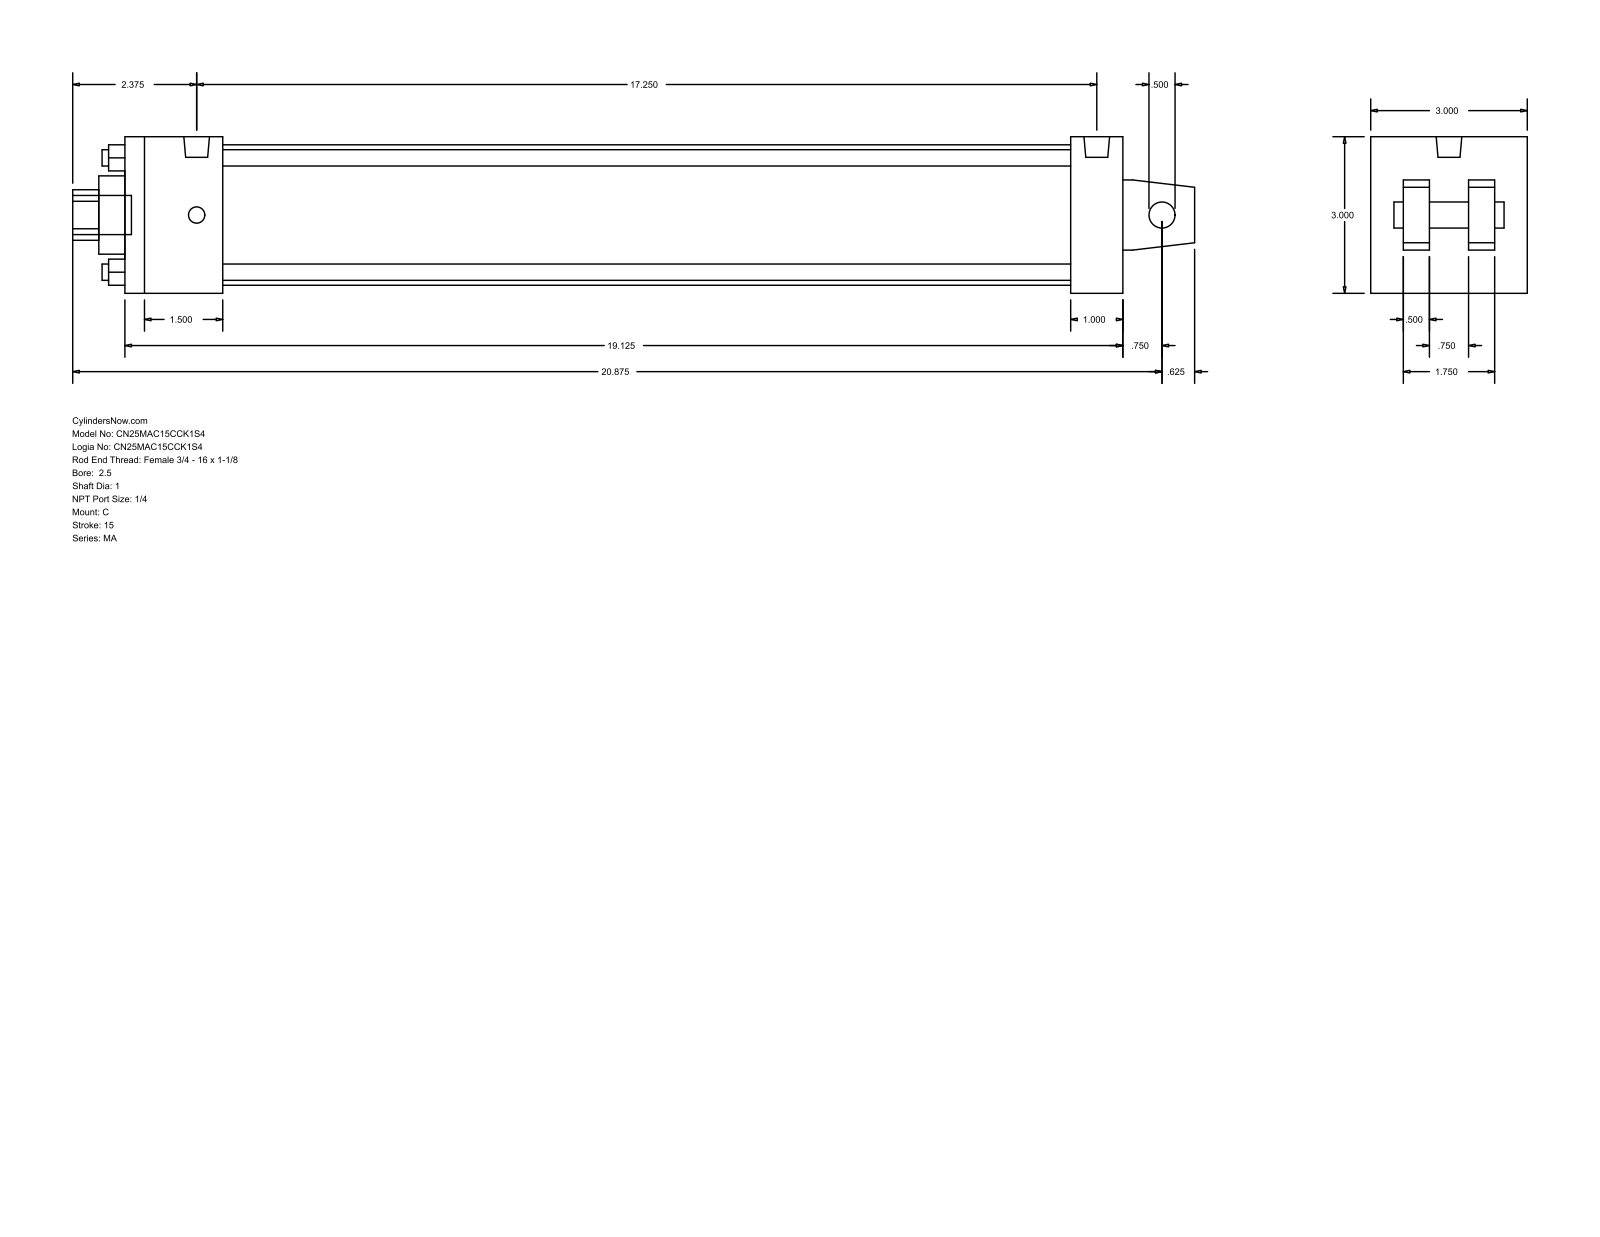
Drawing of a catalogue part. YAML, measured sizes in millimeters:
part_name: "MA_C__0250_1"
step_written_by: "GSSL Pune (CONFIG_CONTROL_DESIGN)"
units: millimeters
bodies: {solids: 0, faces: 103, planar: 76, cylindrical: 27, other: 0}
overall_size: [546.1, 76.2, 76.2]
round_holes:
  - {diameter: 7.94, count: 4}
  - {diameter: 12.7, count: 1}
  - {diameter: 25.4, count: 1}
  - {diameter: 38.1, count: 1}
  - {diameter: 68.33, count: 1}
round_bosses_or_shafts:
  - {diameter: 7.94, count: 4}
  - {diameter: 12.49, count: 2}
  - {diameter: 19.05, count: 1}
partial_cylinders:
  - {radius: 12.29, count: 1}
face_to_face_distances: [76.2, 47.63, 485.78, 12.7, 60.33, 15.87, 28.57, 460.37, 412.74, 438.15]
hole_center_spacings: [39.33, 55.62, 78.66]
